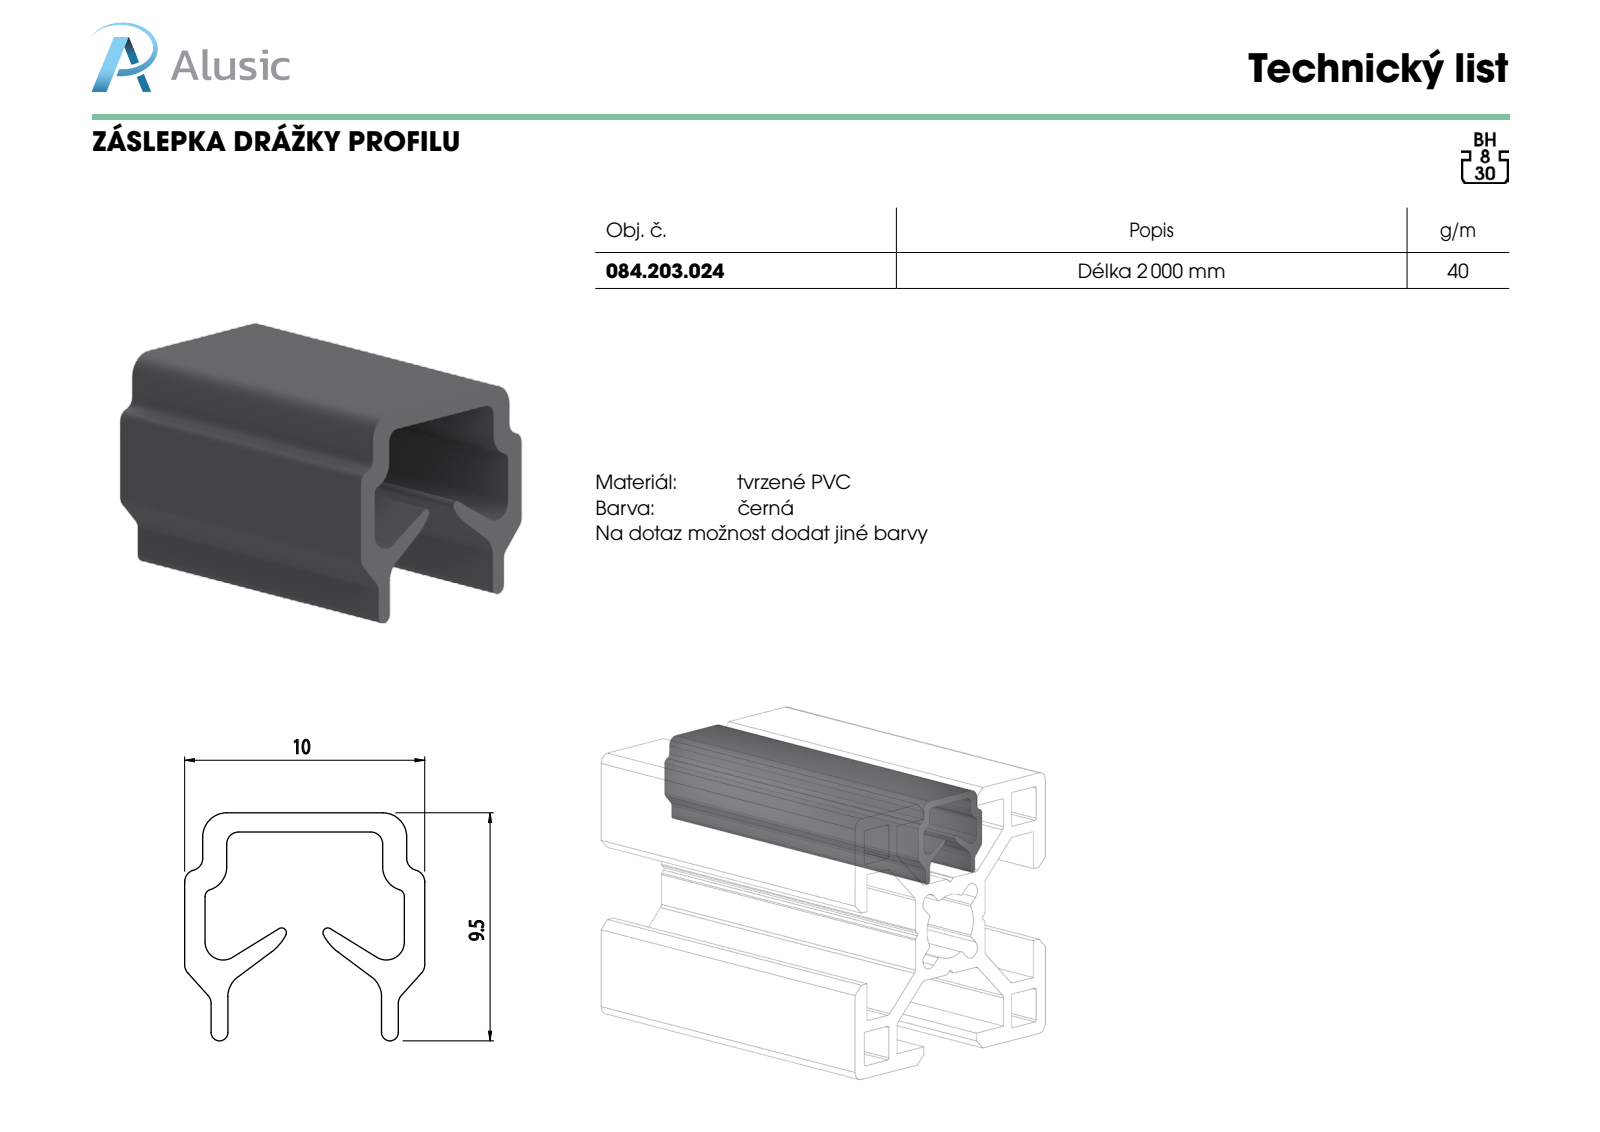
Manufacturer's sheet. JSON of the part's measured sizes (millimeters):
{"part_name": "084.203.024", "step_written_by": "SolidWorks 2012 (CONFIG_CONTROL_DESIGN)", "units": "millimeters", "bodies": {"solids": 1, "faces": 56, "planar": 26, "cylindrical": 30, "other": 0}, "overall_size": [100, 10, 9.5], "volume_mm3": 2832, "surface_area_mm2": 6526, "partial_cylinders_radius": [[0.5, 10], [1, 6], [0.2, 2], [0.3, 2], [0.35, 2], [0.75, 2], [2, 2]], "face_to_face_distances": [0.8, 0.85, 9.15, 10, 1.8, 8.2, 0.95, 7.35, 1.1, 8.9]}
